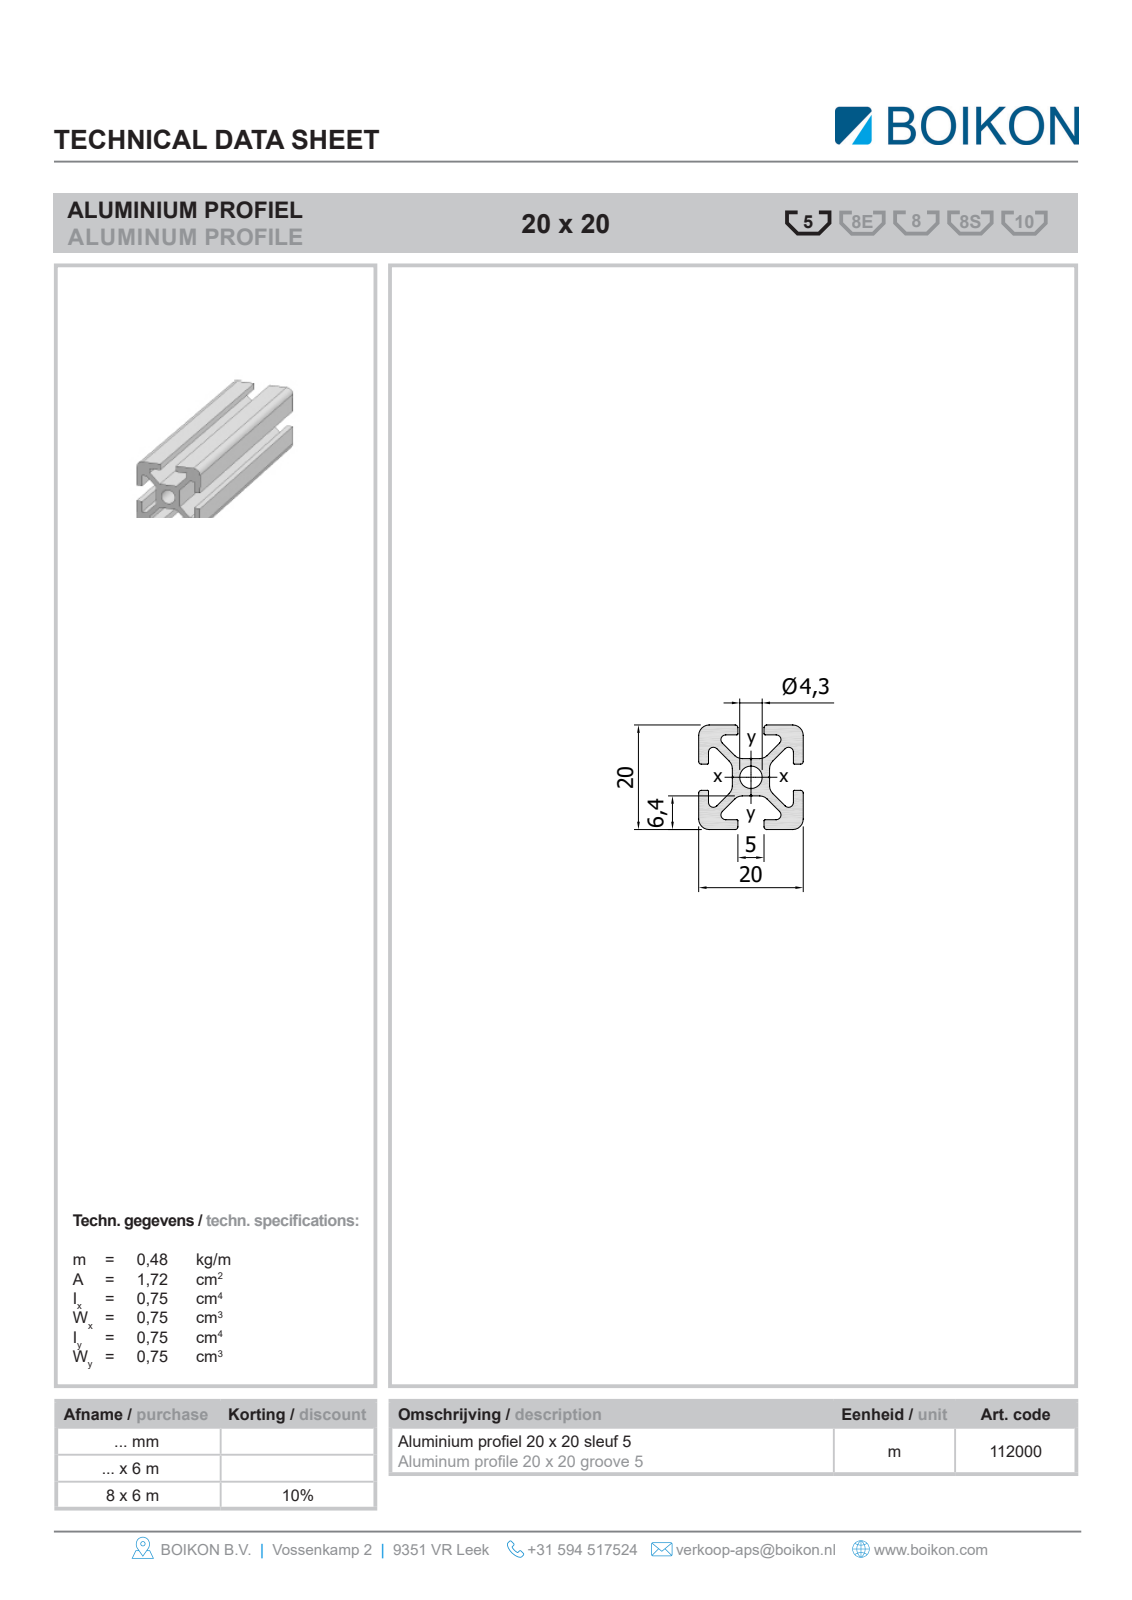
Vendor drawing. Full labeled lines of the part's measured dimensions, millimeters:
Part name (STEP PRODUCT): Root; 11200020x20BOIKON0
STEP written by: HiCAD 2013 1802.4 Build 509 (AUTOMOTIVE_DESIGN)
Units: millimetres
Bodies: 1 solid, 51 faces (46 planar, 5 cylindrical, 0 other)
Overall size (bounding box): 1000 × 20 × 20
Volume: 177 203 mm³ · Surface area: 178 818 mm²
Round holes (diameter × count): ⌀4.3 ×1
Partial cylindrical surfaces — rounded edges, fillets, slot ends (radius × count): R2 ×4
Main face-to-face distances: 1.8, 18.2, 20, 13.7, 11.9, 6.3, 4.5, 1.5, 7.5, 12.5
